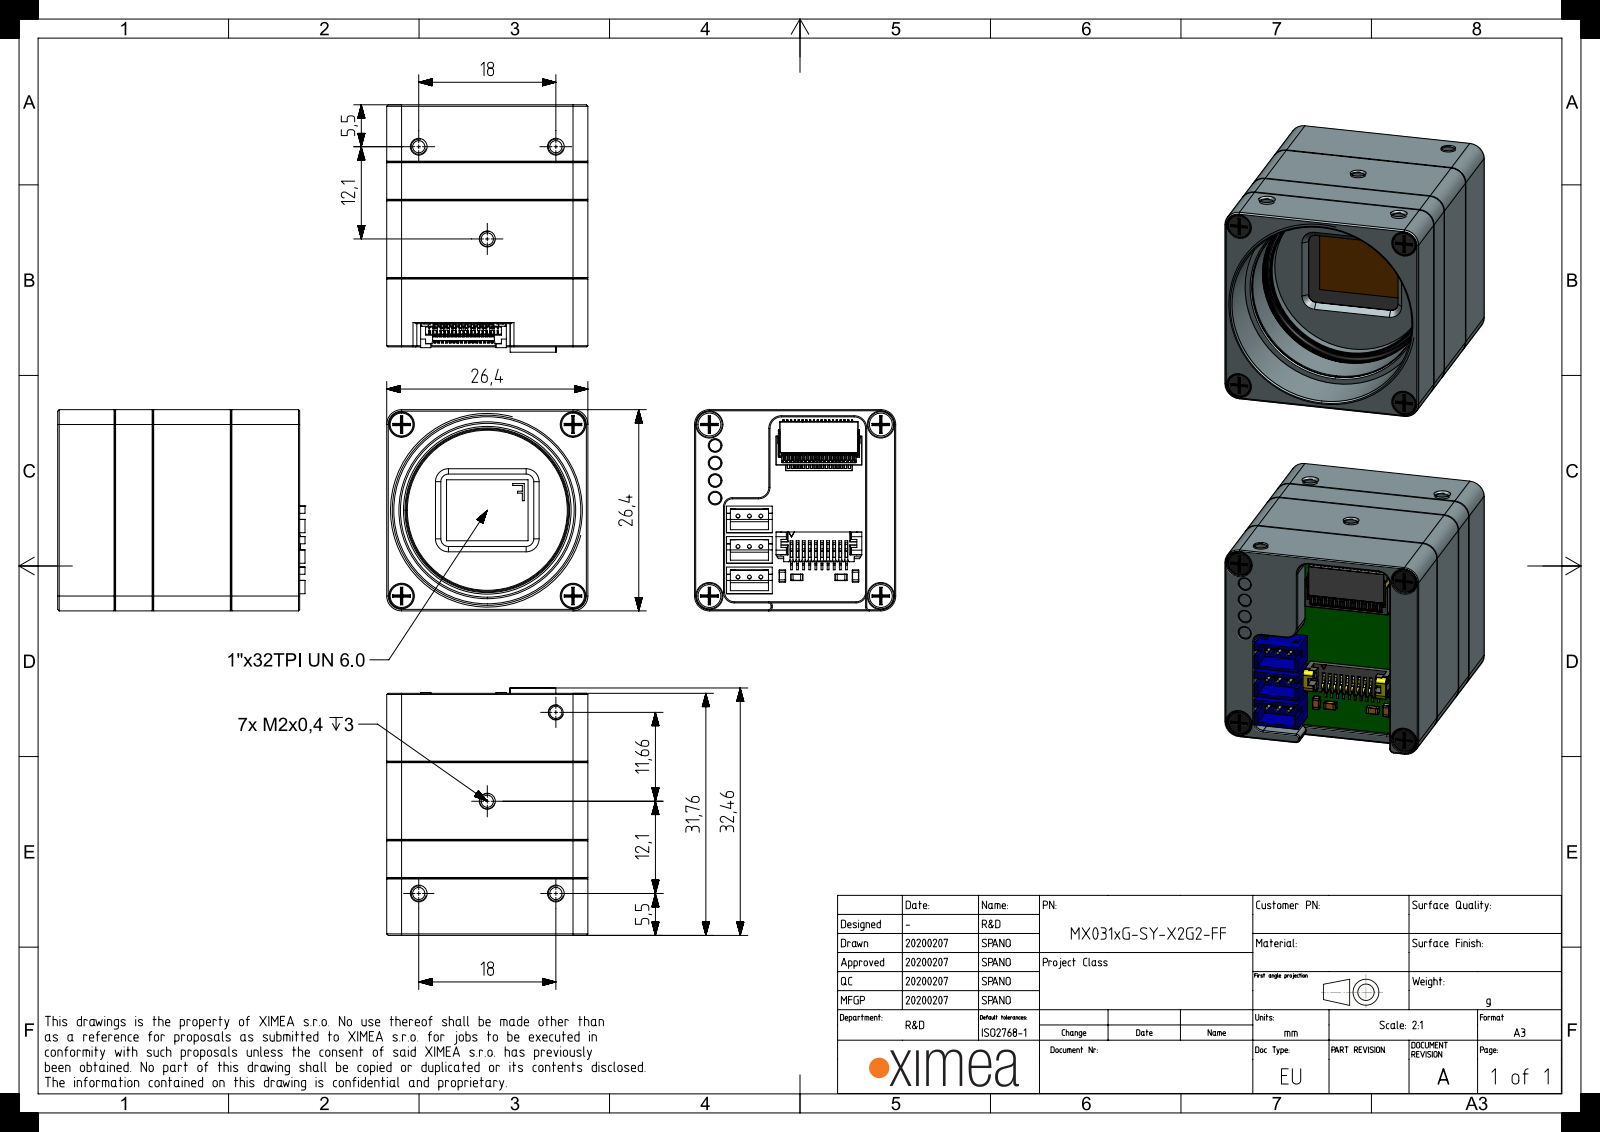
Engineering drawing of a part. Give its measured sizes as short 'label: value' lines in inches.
name: MX-X2G2-MAIN-FF-PCA-REV2; MECH-THERM-PAD-10X5X1; SROB-M2x4-CUST; MX-X2G2-CONN-FF-PCA (+8 more)
written by: SIEMENS PLM Software NX 1907 (AUTOMOTIVE_DESIGN)
unit: in
bodies: 306 solids, 20238 faces (11952 planar, 5731 cylindrical, 2555 other)
size: 1.278 × 1.039 × 1.039
volume: 0.699 in³; area: 35.63 in²
holes: 16× ⌀0.063, 9× ⌀0.028, 8× ⌀0.079, 4× ⌀0.035, 4× ⌀0.035, 4× ⌀0.071, 4× ⌀0.083, 4× ⌀0.118, 4× ⌀0.126, 4× ⌀0.132, 3× ⌀0.012, 2× ⌀0.024
bosses: 9× ⌀0.02, 8× ⌀0.075, 6× ⌀0.118, 4× ⌀0.064, 4× ⌀0.033, 2× ⌀0.063, 2× ⌀0.031, 1× ⌀0.984
rounds: 77× R0.004, 74× R0.005, 30× R0.006, 30× R0.013, 27× R0.015, 22× R0.059, 18× R0.039, 15× R0.008
face distances: 0.039, 0.138, 1.039, 0.178, 0.165, 0.27, 0.447, 0.408, 0.304, 0.224
hole spacings: 0.626, 0.059, 0.15, 0.168, 0.508, 0.515, 0.717, 0.739
